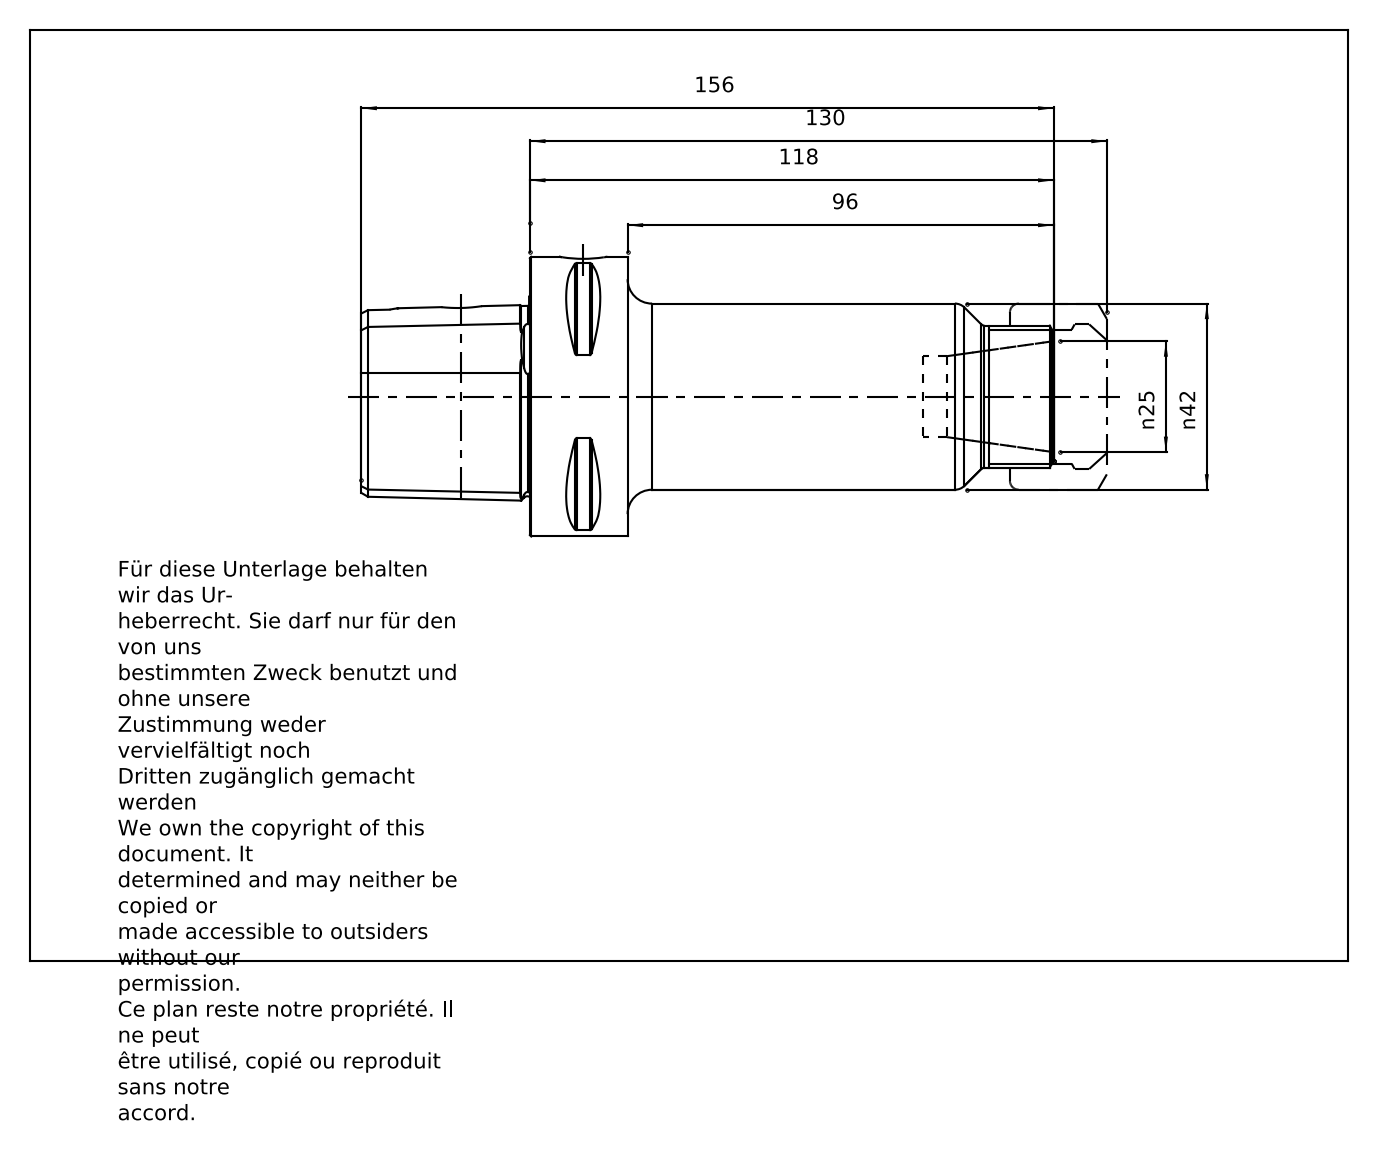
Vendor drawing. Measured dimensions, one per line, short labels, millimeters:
name: CC6-024-25; 83-912-25; CC6-024-25_ASM
written by: PRO/ENGINEER BY PARAMETRIC TECHNOLOGY CORPORATION, 2010430 (CONFIG_CONTROL_DESIGN)
unit: mm
bodies: 2 solids, 170 faces (43 planar, 37 cylindrical, 90 other)
size: 168 × 63 × 63
volume: 234 253 mm³; area: 39 710 mm²
holes: 1× ⌀4.25, 1× ⌀8.1, 1× ⌀10.04, 1× ⌀18, 1× ⌀28.02, 1× ⌀32
bosses: 1× ⌀63, 1× ⌀42, 1× ⌀20
rounds: 8× R0.5, 1× R6
face distances: 110, 22, 88, 20, 130, 108, 38, 60, 148, 168
hole spacings: 27.5
